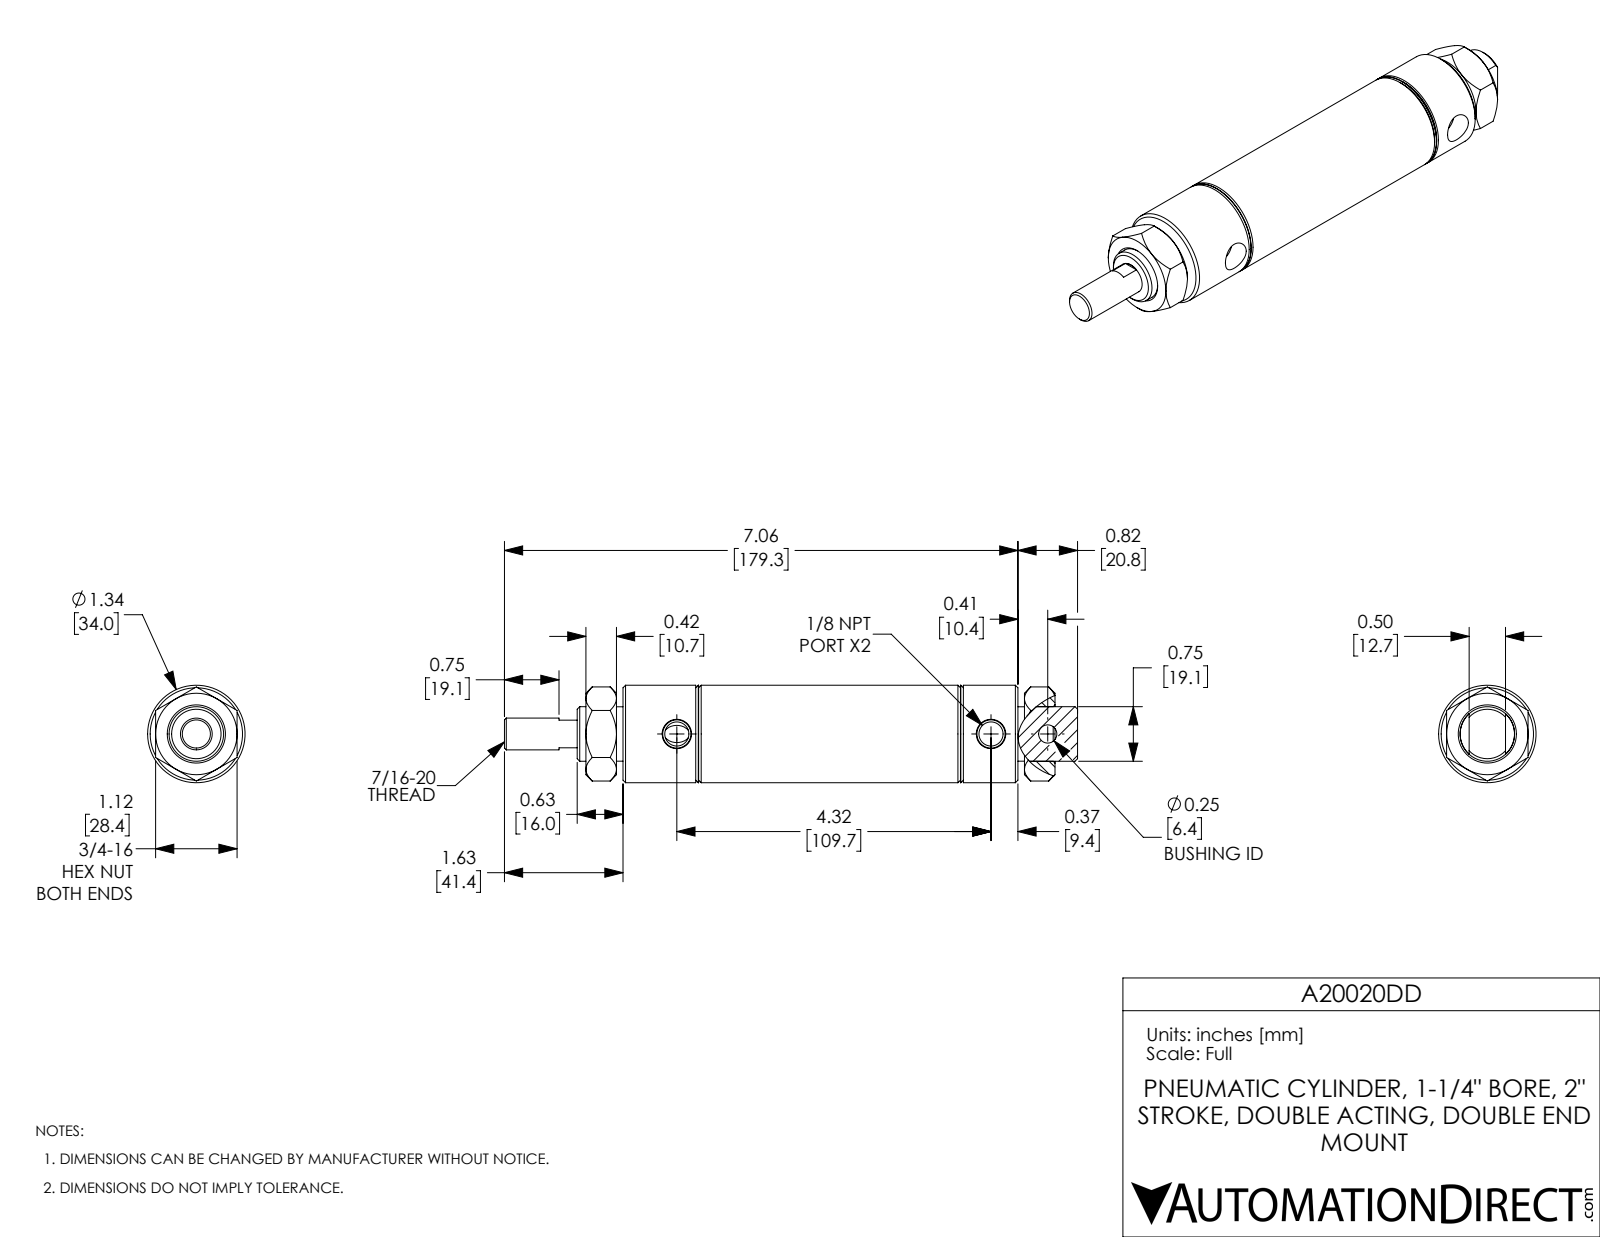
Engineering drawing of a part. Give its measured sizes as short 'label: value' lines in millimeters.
name: A20020DD; A20020DD_Mounting Nut_D-3556; A20020DD-Rod; A20020DD-MainBody
written by: SolidWorks 2017 (AUTOMOTIVE_DESIGN)
unit: mm
bodies: 4 solids, 138 faces (44 planar, 36 cylindrical, 58 other)
size: 200.2 × 34 × 34
volume: 108 200 mm³; area: 41 530 mm²
holes: 2× ⌀8.4, 1× ⌀6.4, 1× ⌀11.1, 1× ⌀19.1, 1× ⌀31.8
bosses: 1× ⌀34, 1× ⌀19
face distances: 37.2, 100.7, 12.7, 28.4, 63.5, 50.8, 7.9, 10.7, 153.2, 49.9
hole spacings: 19.8, 109.7, 129.5
